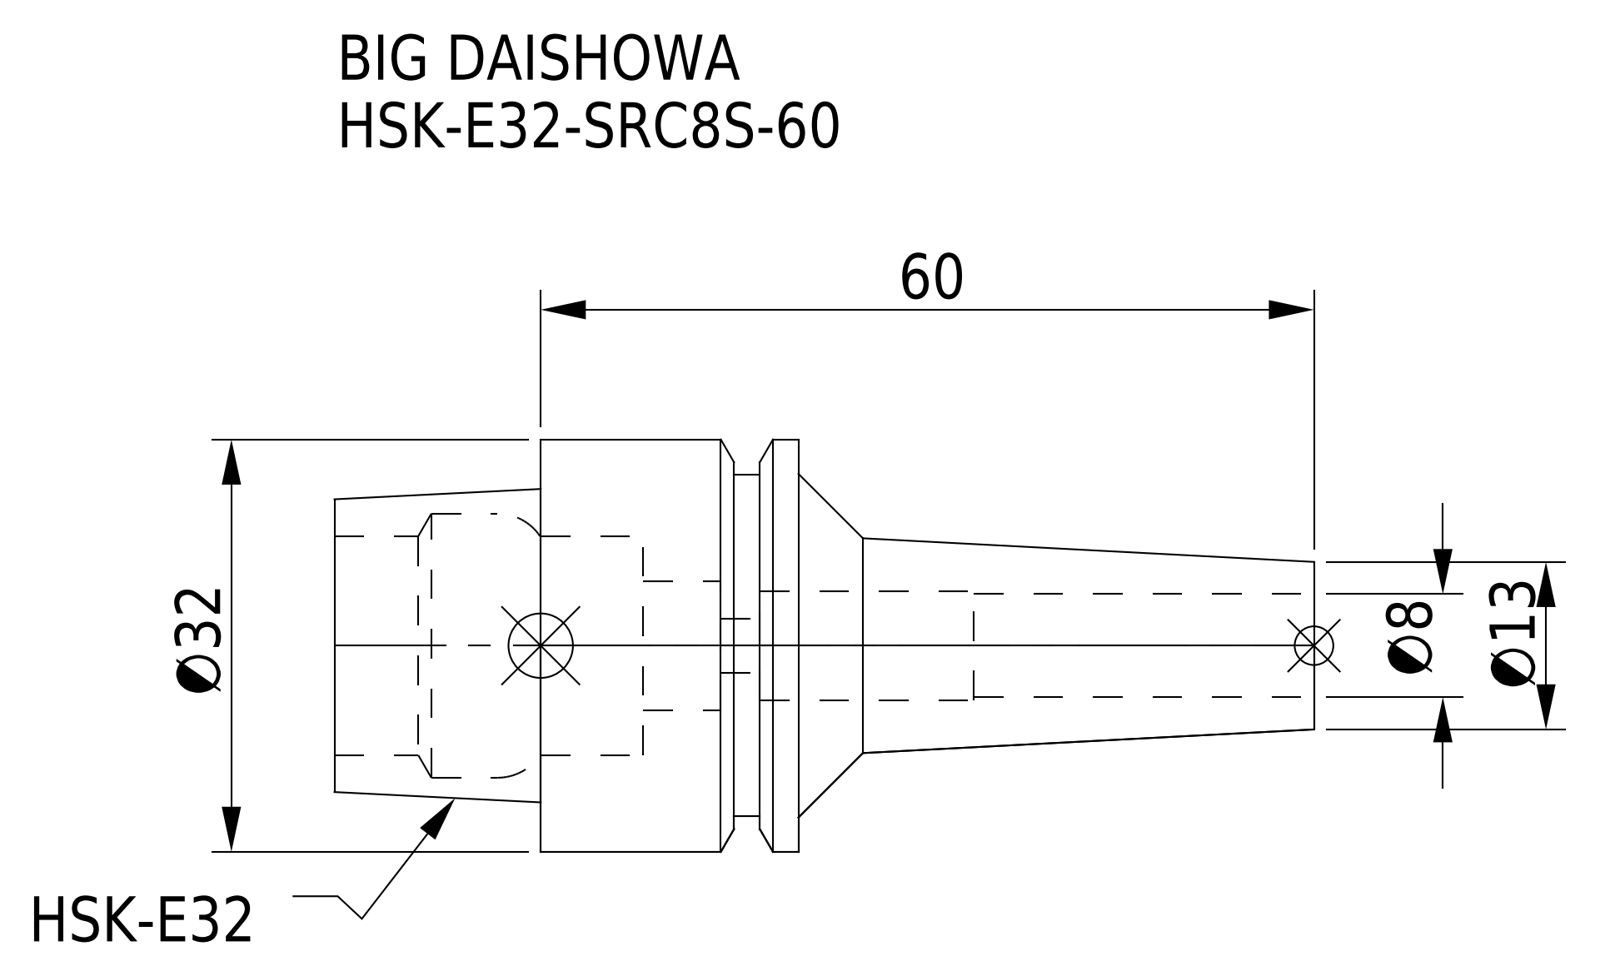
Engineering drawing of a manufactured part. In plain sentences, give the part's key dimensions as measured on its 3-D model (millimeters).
The part is named "HSK-E32-SRC8S-60". Its 3-D file was written by "CREO PARAMETRIC BY PTC INC, 2016380 (AUTOMOTIVE_DESIGN)". It is 1 solid with 46 faces: 10 planar, 22 cylindrical and 14 other. Overall it measures 76 by 32 by 32 millimeters. Its volume is 21 282 cubic millimeters and its surface area 9 531 square millimeters. Round holes: 1 of diameter 4.2, 1 of diameter 8, 1 of diameter 8.5, 1 of diameter 10, 1 of diameter 17, 1 of diameter 20.5. Round bosses or shafts: 1 of diameter 32, 1 of diameter 26.5. The main face-to-face distances are 20, 36, 16, 12.05, 7.95, 23.95, 3, 9.05, 17, 33.
